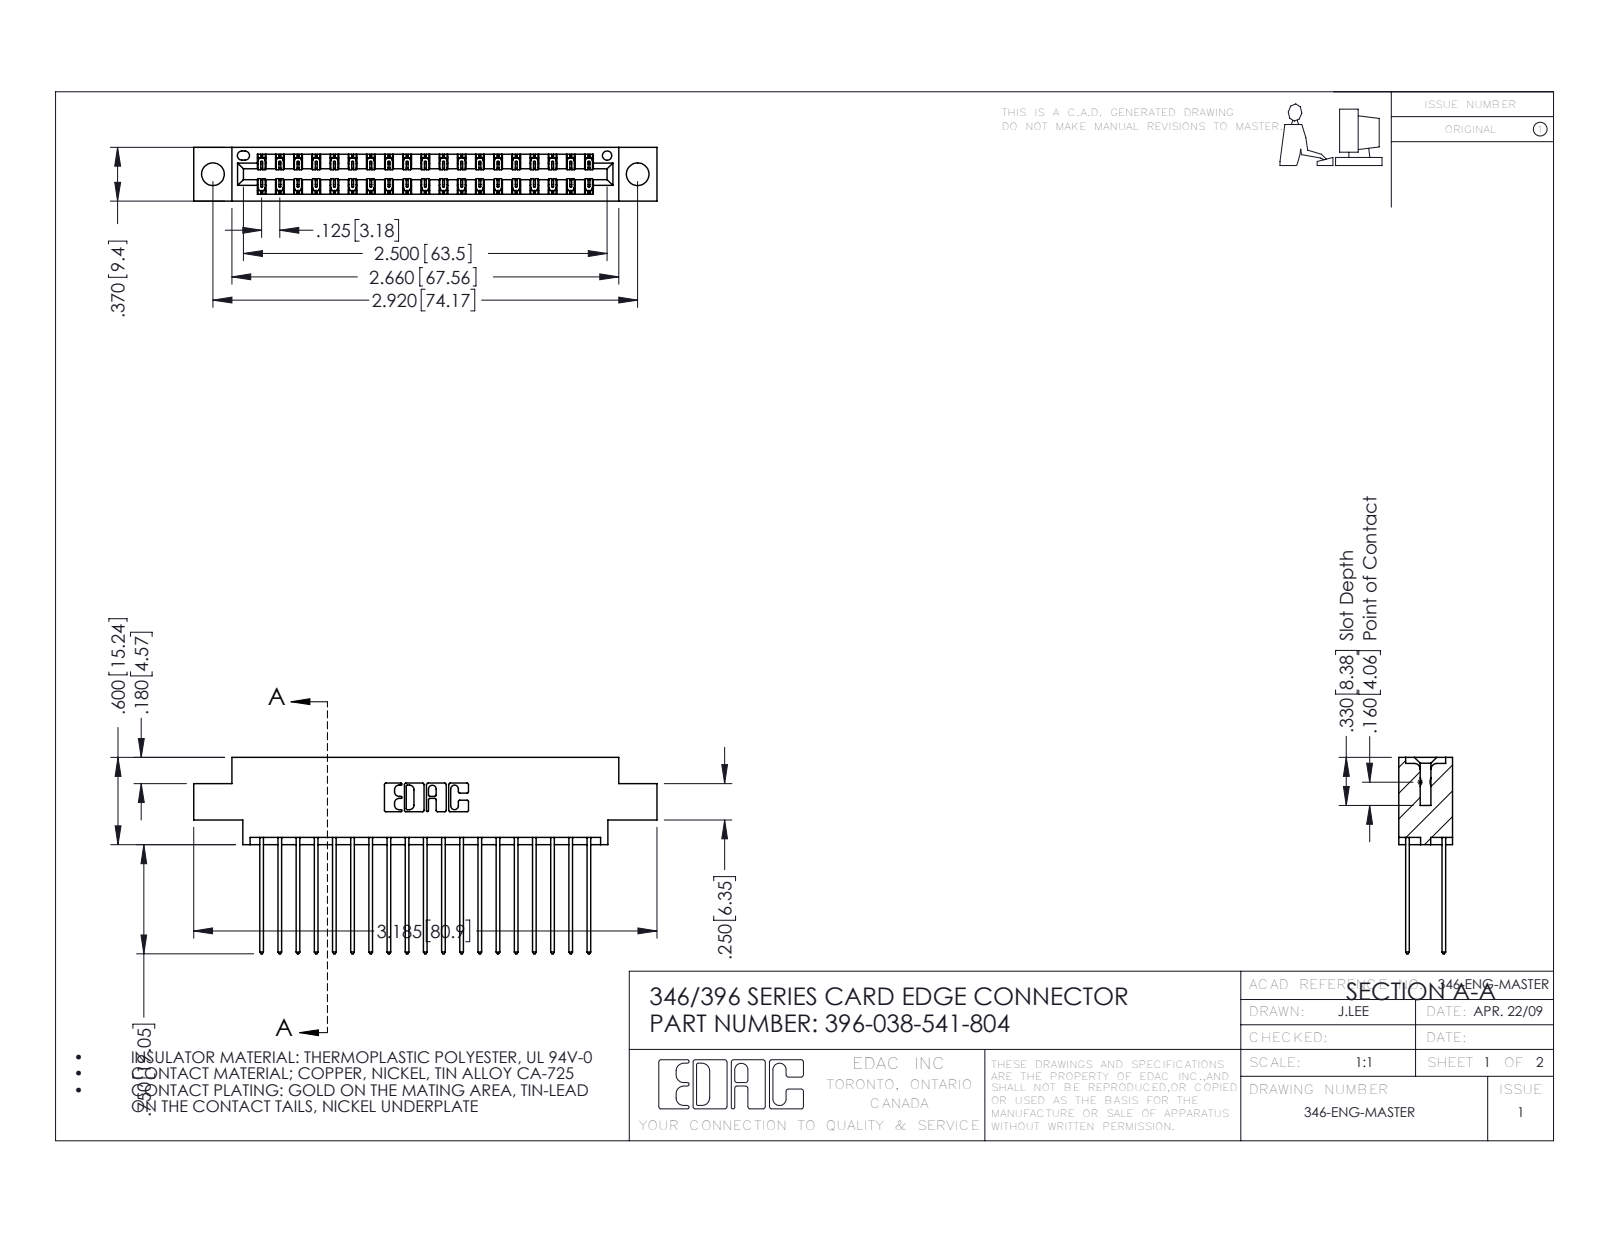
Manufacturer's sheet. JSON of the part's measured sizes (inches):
{"part_name": "396-038-541-804; 345-292-001_345-293-141; 346 Part_0.170 Offset - 0.156 Dia-TH", "step_written_by": "SolidWorks 2016 (CONFIG_CONTROL_DESIGN)", "units": "inches", "bodies": {"solids": 39, "faces": 2102, "planar": 1410, "cylindrical": 692, "other": 0}, "overall_size": [3.185, 1.35, 0.37], "volume_in3": 0.469, "surface_area_in2": 17.42, "round_holes": [[0.156, 2], [0.064, 1]], "partial_cylinders_radius": [[0.006, 57], [0.01, 38], [0.01, 22], [0.007, 6], [0.031, 6], [0.026, 3], [0.014, 2], [0.022, 2]], "face_to_face_distances": [0.048, 0.322, 0.25, 0.072, 0.298, 0.025, 0.37, 0.275, 0.225, 0.148], "hole_center_spacings": [0.246, 2.713, 2.92]}
